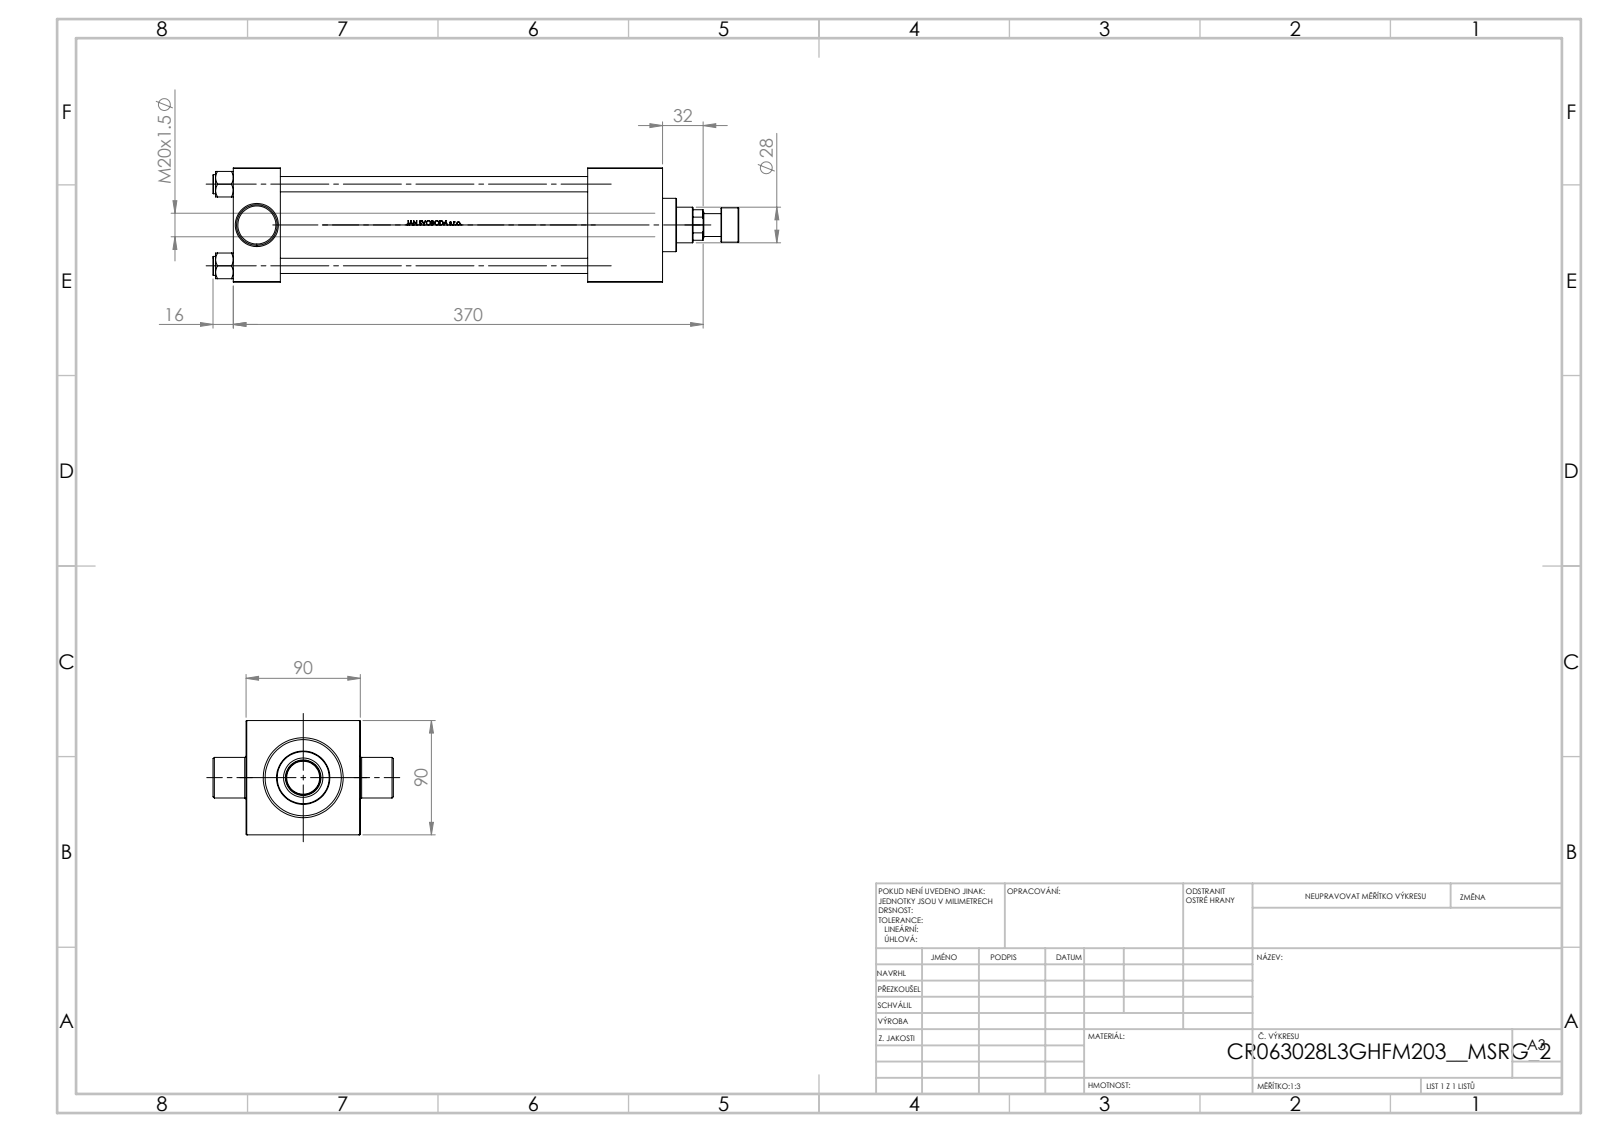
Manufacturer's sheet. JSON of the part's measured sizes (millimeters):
{"part_name": "V215_VC_A; V215CR_L_Body; V215CR_VCP_L; V215CR_L_TYCINKA (+2 more)", "step_written_by": "SolidWorks 2019 (CONFIG_CONTROL_DESIGN)", "units": "millimeters", "bodies": {"solids": 12, "faces": 1071, "planar": 429, "cylindrical": 114, "other": 528}, "overall_size": [414, 142, 90], "volume_mm3": 1324000, "surface_area_mm2": 299557, "round_holes": [[12, 4], [7, 1], [18.5, 1], [28, 1], [31, 1], [50, 1], [60, 1], [63, 1]], "round_bosses_or_shafts": [[15, 4], [69, 1], [42, 1], [32, 1], [27, 1], [18, 1]], "face_to_face_distances": [90, 37, 338, 301, 89, 59, 0.5, 242, 279, 89.5], "hole_center_spacings": [45.47, 64.3, 90.93]}
